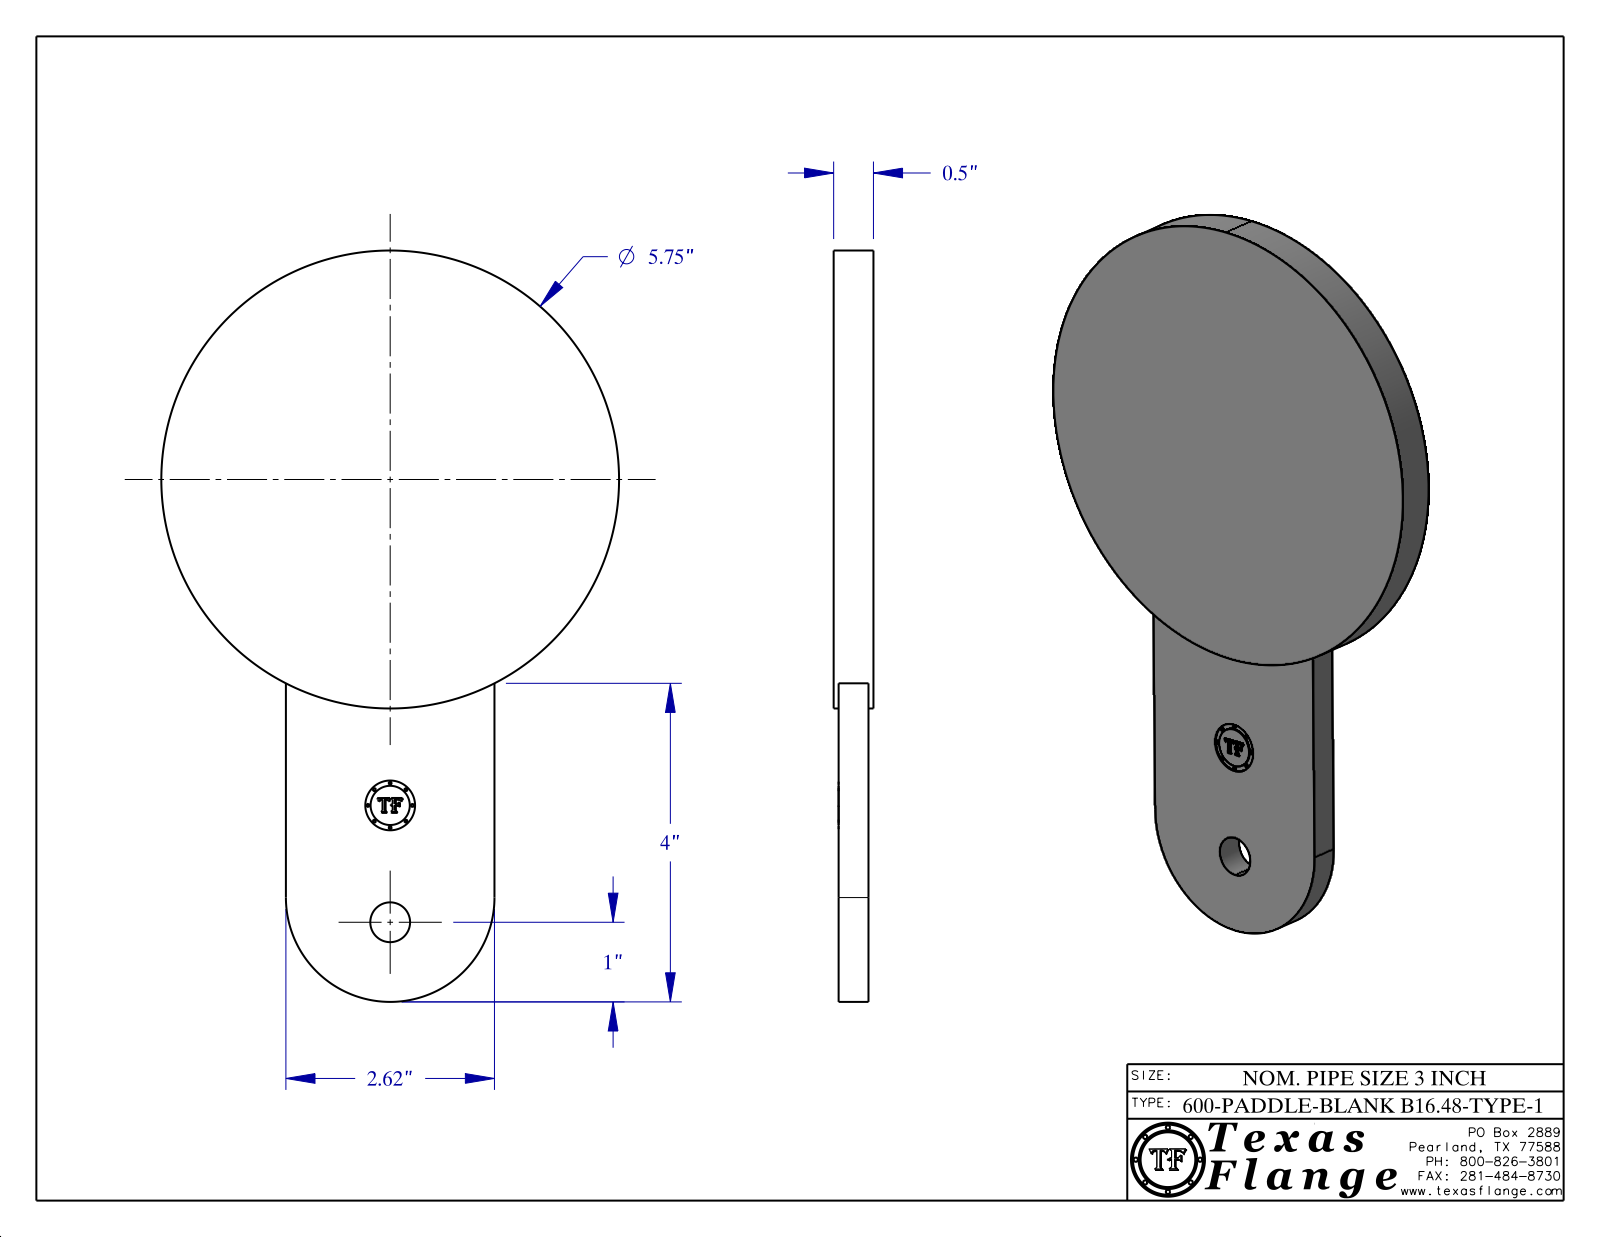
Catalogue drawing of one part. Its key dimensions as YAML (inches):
part_name: "3-600-PADDLE-BLANK-B16.48-TYPE-1"
step_written_by: "CATIA V5 STEP AP214 (AUTOMOTIVE_DESIGN)"
units: inches
bodies: {solids: 1, faces: 396, planar: 371, cylindrical: 25, other: 0}
overall_size: [9.434, 5.75, 0.5]
volume: 16.35
surface_area: 82.19
round_holes:
  - {diameter: 0.5, count: 1}
  - {diameter: 0.625, count: 1}
round_bosses_or_shafts:
  - {diameter: 0.038, count: 8}
  - {diameter: 5.75, count: 1}
  - {diameter: 0.492, count: 1}
partial_cylinders:
  - {radius: 1.31, count: 1}
face_to_face_distances: [0.5, 0.063, 0.437, 0.375, 2.62, 0.422, 0.36, 0.015, 0.078, 1.247]
hole_center_spacings: [1.467]
